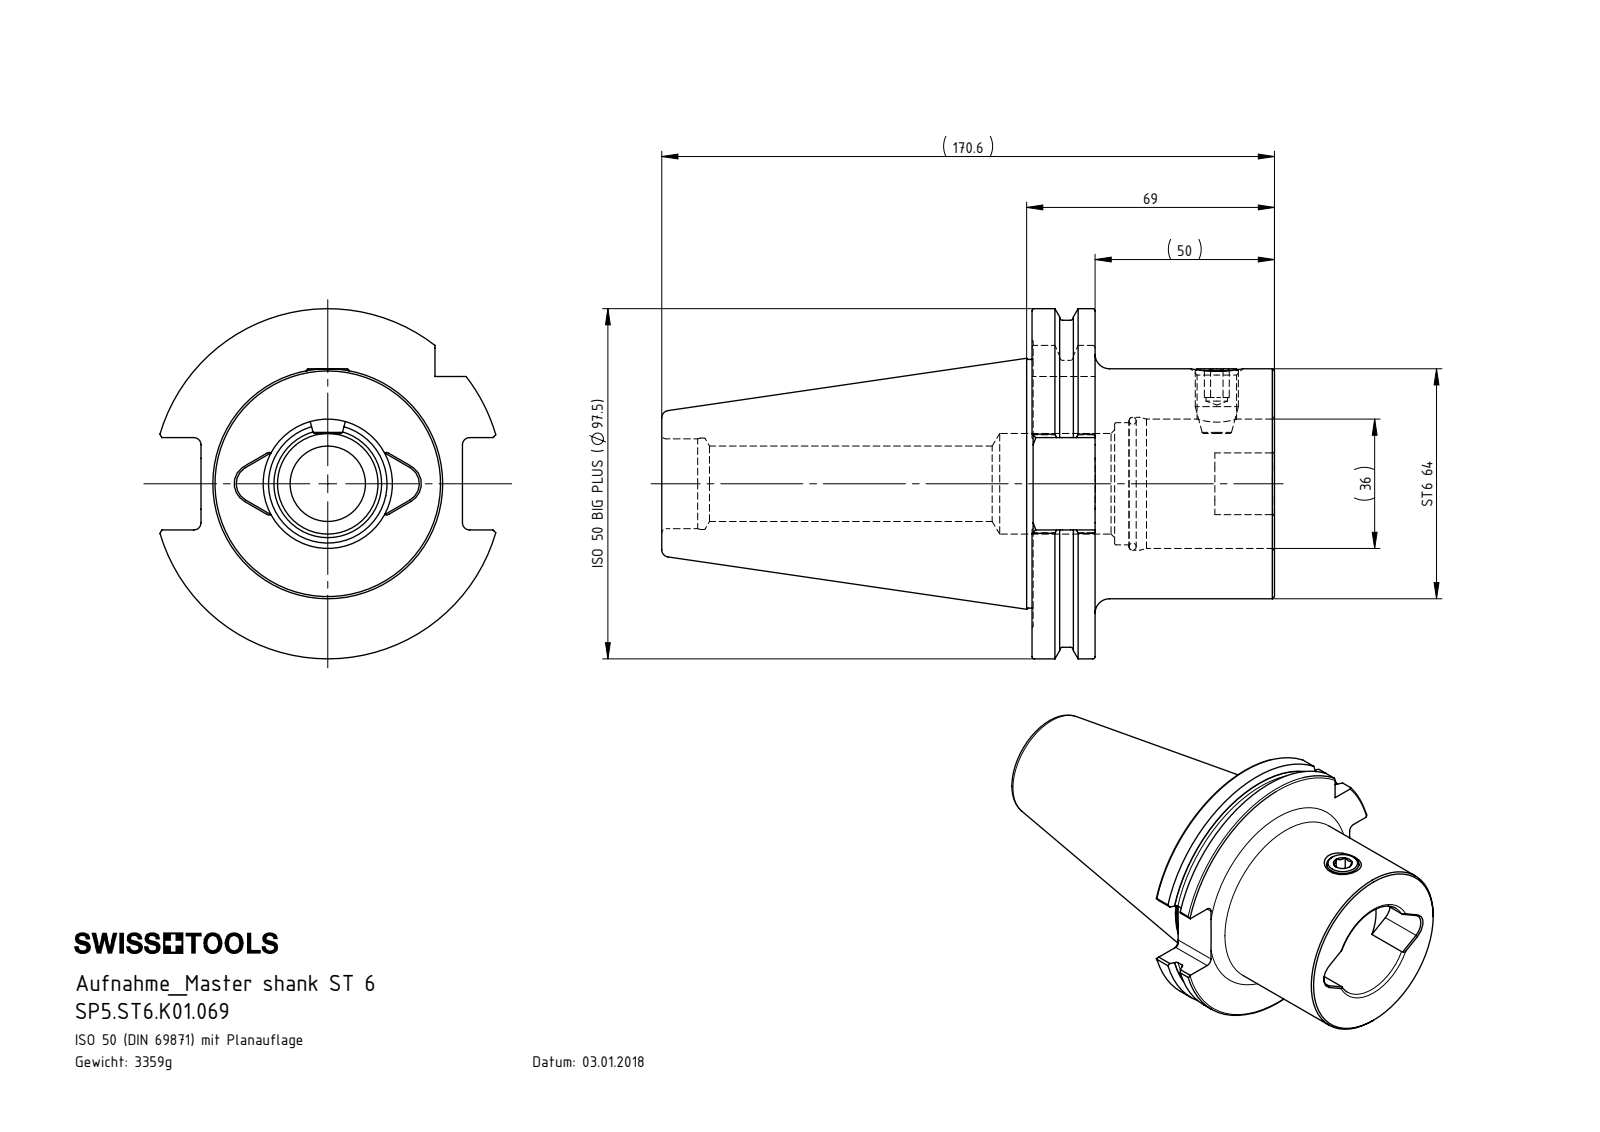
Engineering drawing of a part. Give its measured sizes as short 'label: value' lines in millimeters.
name: SP5-ST6.K01.069_A; SP5.ST6.K01.069; DIN 3771 - 33x2; ST6-ER1.001.018_A
written by: SolidWorks 2017 (AUTOMOTIVE_DESIGN)
unit: mm
bodies: 3 solids, 138 faces (56 planar, 31 cylindrical, 51 other)
size: 170.6 × 97.45 × 93.51
volume: 428 245 mm³; area: 60 984 mm²
holes: 1× ⌀6, 1× ⌀11, 1× ⌀21, 1× ⌀25, 1× ⌀25.45, 1× ⌀28, 1× ⌀34, 1× ⌀36, 1× ⌀37
bosses: 1× ⌀91, 1× ⌀69.2, 1× ⌀64, 1× ⌀12
rounds: 4× R1.9, 4× R2, 2× R5.2, 1× R48.73
face distances: 49.95, 17.55, 67.5, 17.25, 67.2, 103.1, 103.4, 120.65, 170.6, 72.8
